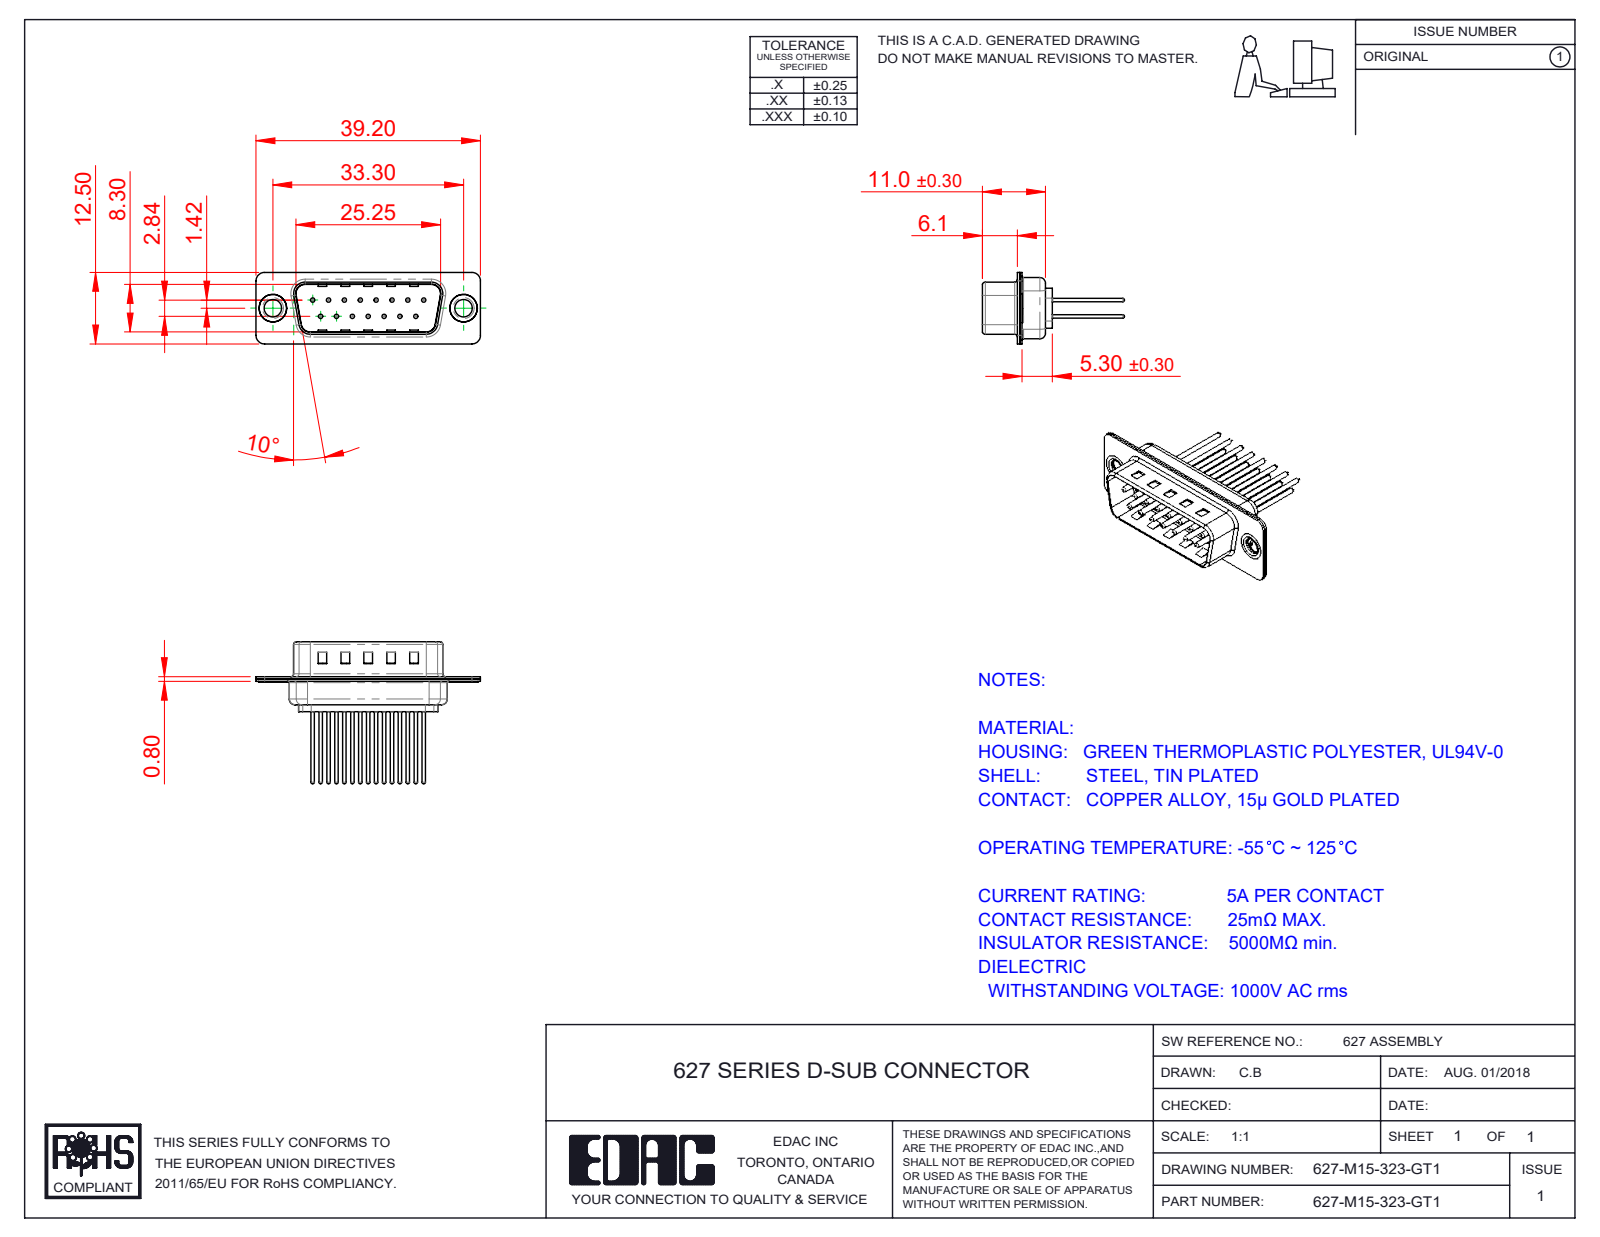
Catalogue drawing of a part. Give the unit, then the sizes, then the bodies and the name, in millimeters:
Units: millimetres
Overall size (bounding box): 39.2 × 24.77 × 12.5
Round holes (diameter × count): ⌀0.75 ×15, ⌀1.6 ×15, ⌀2 ×15, ⌀3.05 ×2, ⌀4 ×2, ⌀4.8 ×2
Round bosses / shafts (diameter × count): ⌀1.5 ×15, ⌀0.6 ×15, ⌀5 ×2, ⌀4.9 ×2, ⌀3.55 ×2
Partial cylindrical surfaces — rounded edges, fillets, slot ends (radius × count): R1.5 ×16, R2 ×12, R0.5 ×8, R1.6 ×8, R0.25 ×4, R0.6 ×4, R0.65 ×4, R0.9 ×4
Main face-to-face distances: 0.4, 0.8, 9.5, 9.1, 8.7, 9.9, 1.2, 6.1, 5.3, 5.7
Hole centre spacings: 3.16, 2.77, 5.54, 8.31, 11.08, 5.03, 5.04, 7.48
Volume: 1 794 mm³ · Surface area: 4 857 mm²
Bodies: 20 solids, 869 faces (244 planar, 327 cylindrical, 298 other)
Part name (STEP PRODUCT): 627M Contact Row 2_23; 627-M15-323-GT1; 627M Thru Hole Rivet; 627M Housing_15 Contacts (+3 more)
STEP written by: SolidWorks 2020 (CONFIG_CONTROL_DESIGN)
